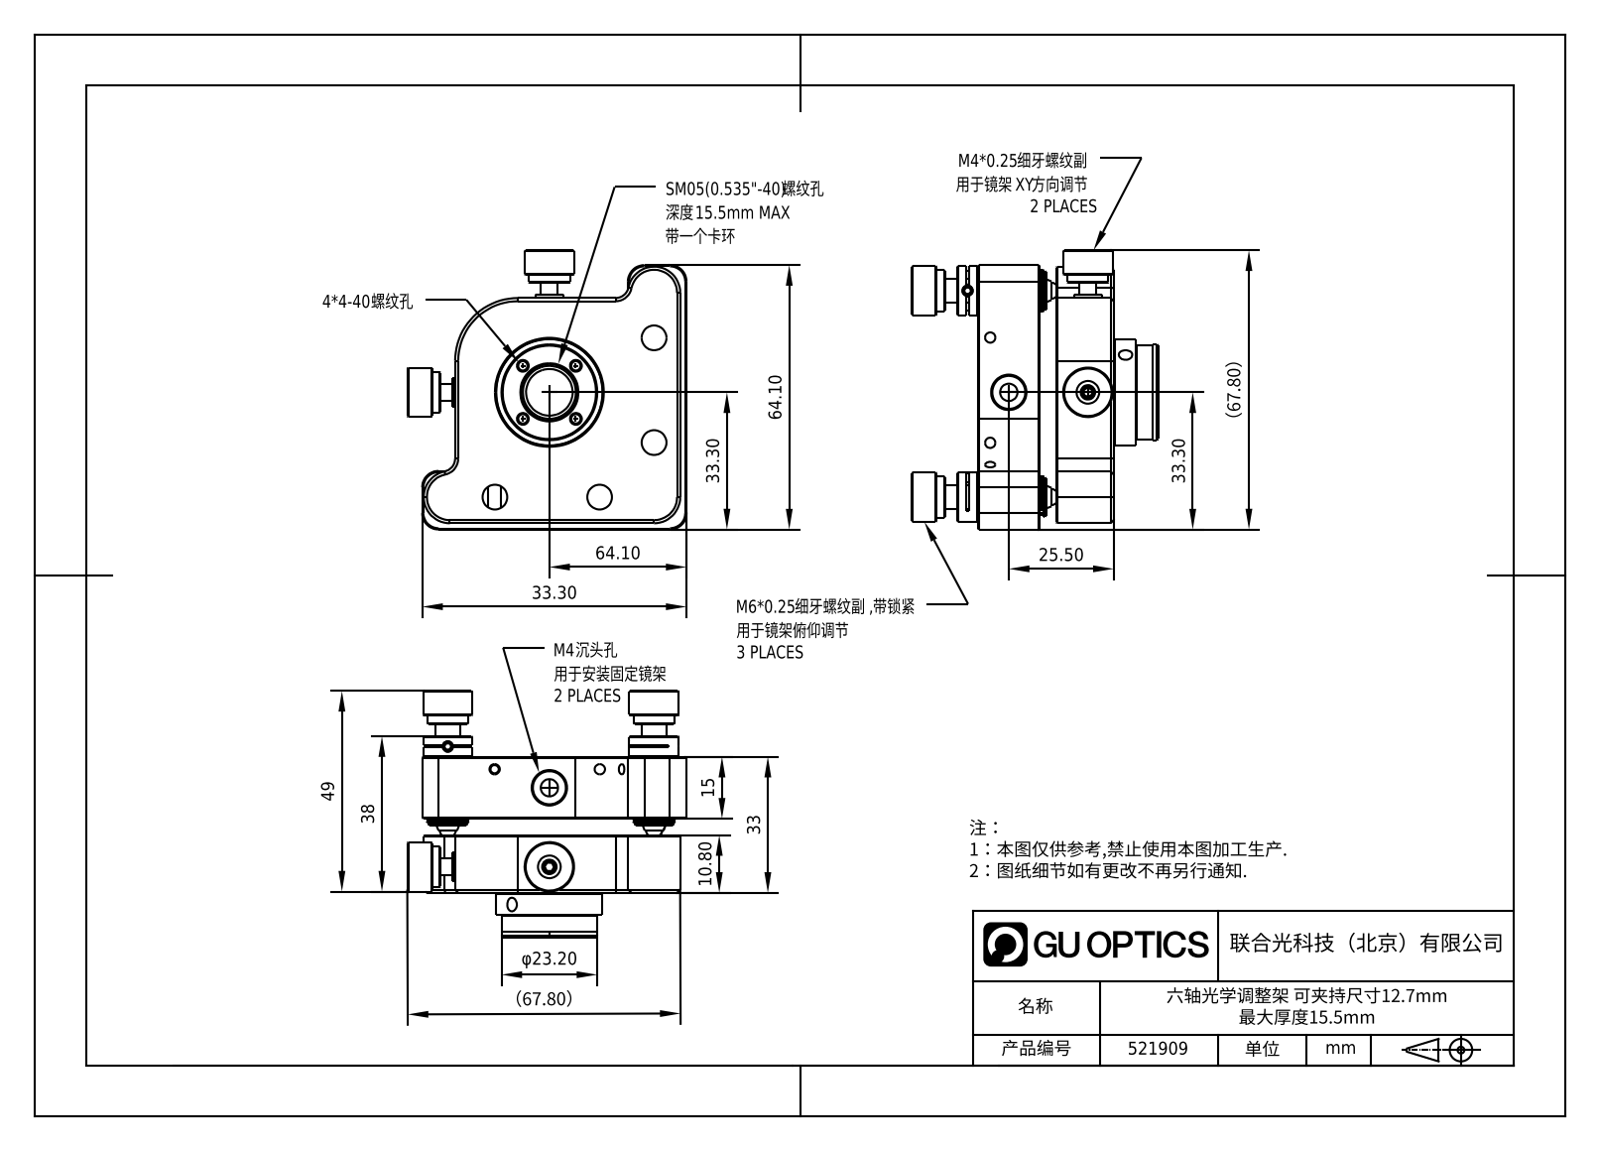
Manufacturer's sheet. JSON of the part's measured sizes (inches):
{"part_name": "1.1.10.17_ZJP-6SM05_六维光学调整镜架，带SM05螺纹，含一个压圈", "step_written_by": "SolidWorks 2021 (CONFIG_CONTROL_DESIGN)", "units": "inches", "bodies": {"solids": 0, "faces": 639, "planar": 132, "cylindrical": 259, "other": 248}, "overall_size": [2.666, 2.666, 2.351], "round_holes": [[0.098, 11], [0.114, 8], [0.039, 4], [0.089, 4], [0.236, 4], [0.157, 3], [0.25, 3], [0.138, 2], [0.165, 2], [0.315, 2], [0.125, 1], [0.13, 1]], "round_bosses_or_shafts": [[0.472, 5], [0.394, 5], [0.118, 4], [0.374, 3], [0.315, 3], [0.236, 3], [0.268, 2], [0.157, 2]], "partial_cylinders_radius": [[0.25, 9], [0.008, 7], [0.235, 6], [0.157, 5], [0.031, 4], [0.125, 3], [0.063, 2], [0.15, 2]], "face_to_face_distances": [0.55, 0.06, 0.157, 0.707, 0.591, 0.748, 1.298, 0.425, 0.873, 0.283], "hole_center_spacings": [0.445, 0.763, 0.779, 0.942, 1.102, 1.128, 0.102, 0.358]}
